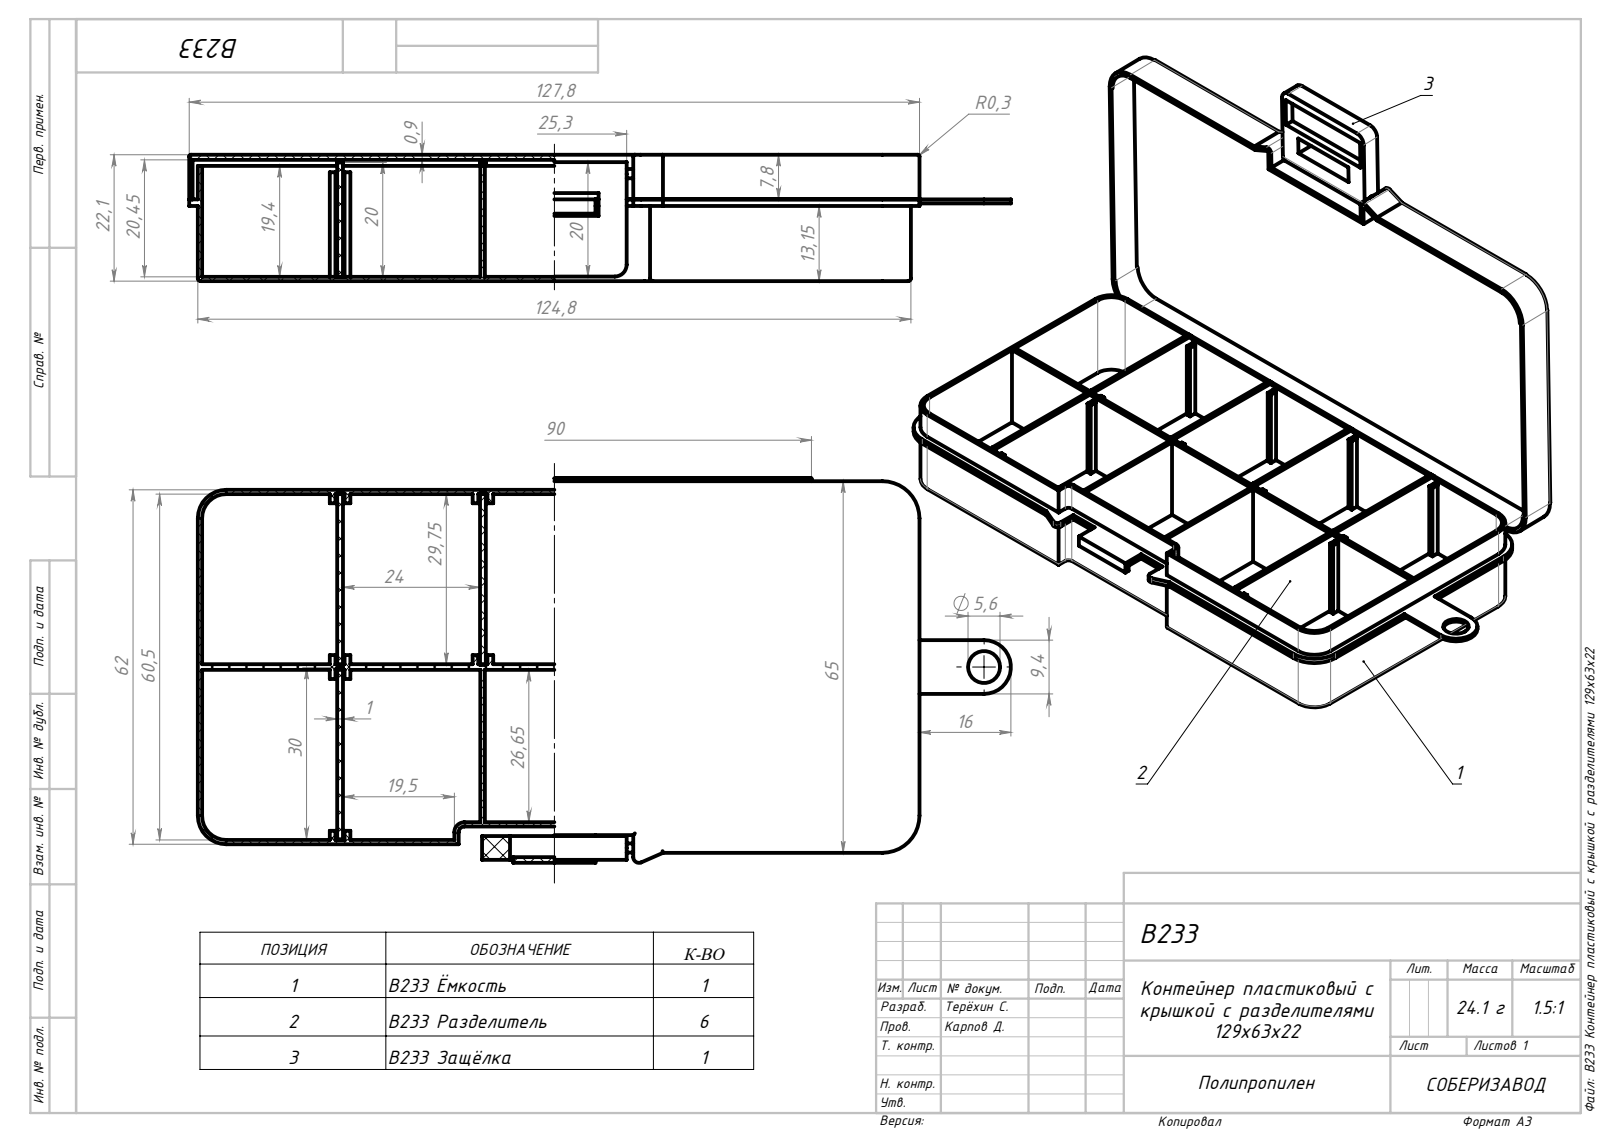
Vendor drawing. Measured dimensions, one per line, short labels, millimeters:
name: B233 Ёмкость; B233 Контейнер пластиковый с крышкой с разделителями 129x63x22; B233 Защёлка; B233 Разделитель (+1 more)
written by: SolidWorks 2021 (AUTOMOTIVE_DESIGN)
unit: mm
bodies: 9 solids, 326 faces (240 planar, 68 cylindrical, 18 other)
size: 143.8 × 67.25 × 22.1
volume: 30 515 mm³; area: 71 032 mm²
holes: 1× ⌀1.99, 1× ⌀5.6
bosses: 1× ⌀1.6
rounds: 9× R0.3, 7× R0.5, 4× R1, 4× R4.25, 4× R5, 4× R5.6, 4× R6.5, 3× R2.08
face distances: 0.75, 0.9, 21.2, 22.1, 20.45, 21.35, 1, 31.5, 30.5, 25
